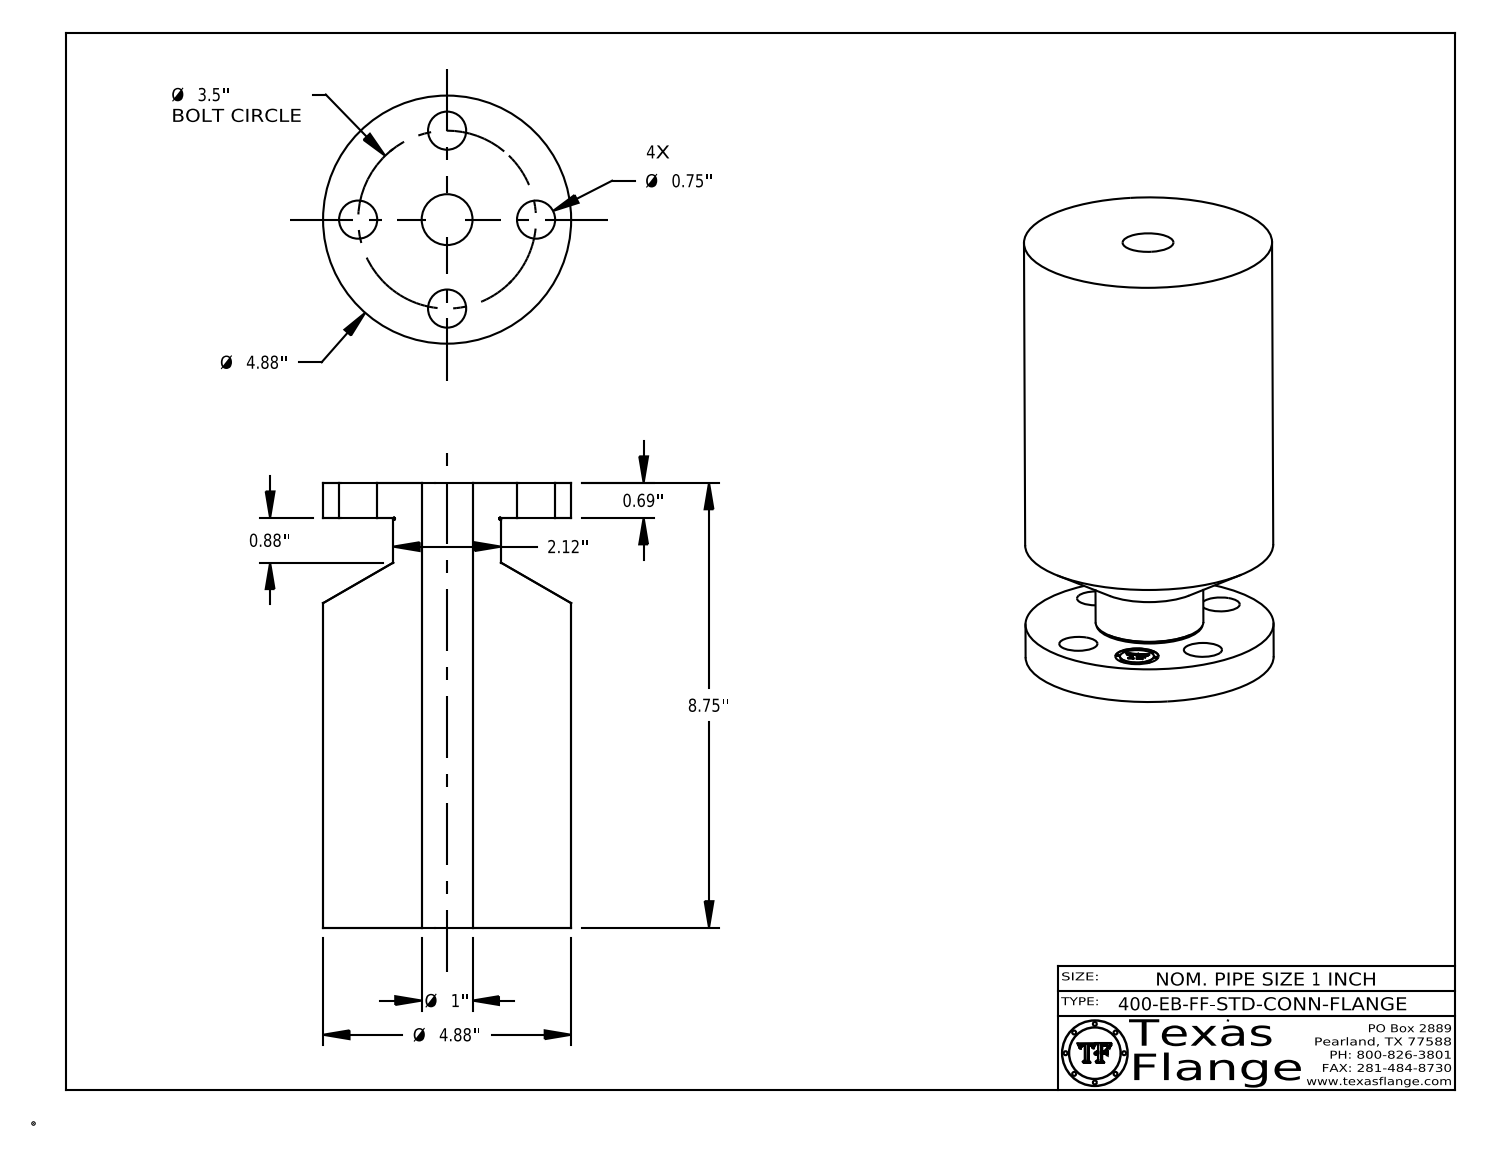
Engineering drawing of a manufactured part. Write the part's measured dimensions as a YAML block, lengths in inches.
part_name: "1-400-EB-FF-STD-CONN-FLANGE"
step_written_by: "CATIA V5 STEP AP214 (AUTOMOTIVE_DESIGN)"
units: inches
bodies: {solids: 1, faces: 410, planar: 368, cylindrical: 36, other: 6}
overall_size: [8.75, 4.88, 4.88]
volume: 135.4
surface_area: 213.6
round_holes:
  - {diameter: 0.75, count: 4}
  - {diameter: 0.85, count: 1}
  - {diameter: 1, count: 1}
round_bosses_or_shafts:
  - {diameter: 0.051, count: 8}
  - {diameter: 4.88, count: 1}
  - {diameter: 2.12, count: 1}
  - {diameter: 0.67, count: 1}
face_to_face_distances: [8.75, 0.69, 8.06, 0.685, 8.065, 0.016, 0.254, 0.249, 0.046, 0.165]
hole_center_spacings: [1.75, 2.475, 1.339, 3.233, 3.5]
